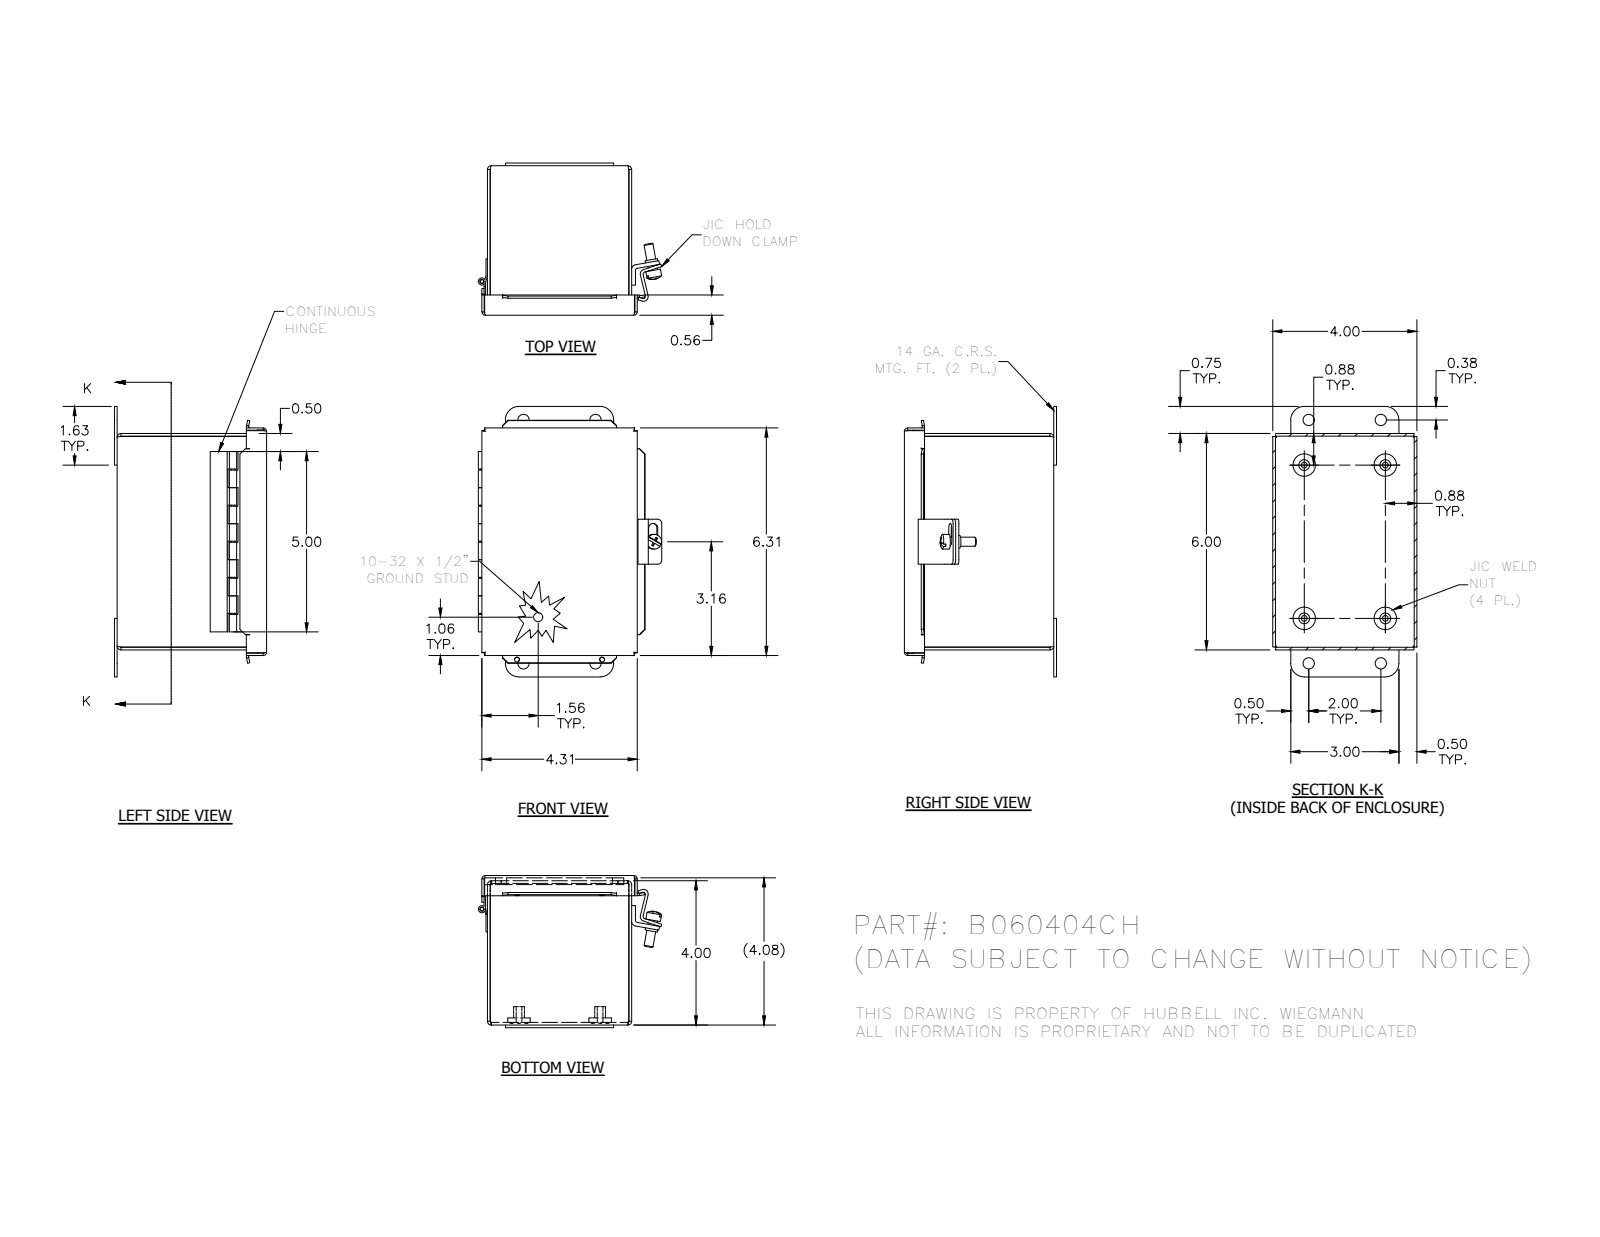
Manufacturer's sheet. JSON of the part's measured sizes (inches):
{"part_name": "B060404CH; 3499; 3481; C1001 (+8 more)", "step_written_by": "Autodesk Inventor 2012 (AUTOMOTIVE_DESIGN)", "units": "inches", "bodies": {"solids": 17, "faces": 386, "planar": 253, "cylindrical": 91, "other": 42}, "overall_size": [7.5, 5.087, 4.219], "volume_in3": 14.03, "surface_area_in2": 379.8, "round_holes": [[0.156, 4], [0.31, 4], [0.14, 2], [0.116, 1], [0.196, 1]], "round_bosses_or_shafts": [[0.625, 4], [0.3, 4], [0.25, 2], [0.41, 1], [0.344, 1], [0.2, 1], [0.19, 1], [0.1, 1]], "partial_cylinders_radius": [[0.031, 15], [0.105, 8], [0.093, 7], [0.125, 4], [0.375, 4], [0.063, 3], [0.126, 3], [0.133, 2]], "face_to_face_distances": [0.074, 3.926, 4.083, 5.926, 4, 3.852, 4.144, 0.062, 4.009, 4.07], "hole_center_spacings": [2.466, 1.256, 1.257, 2, 5.502, 5.502, 5.897, 6.75]}
